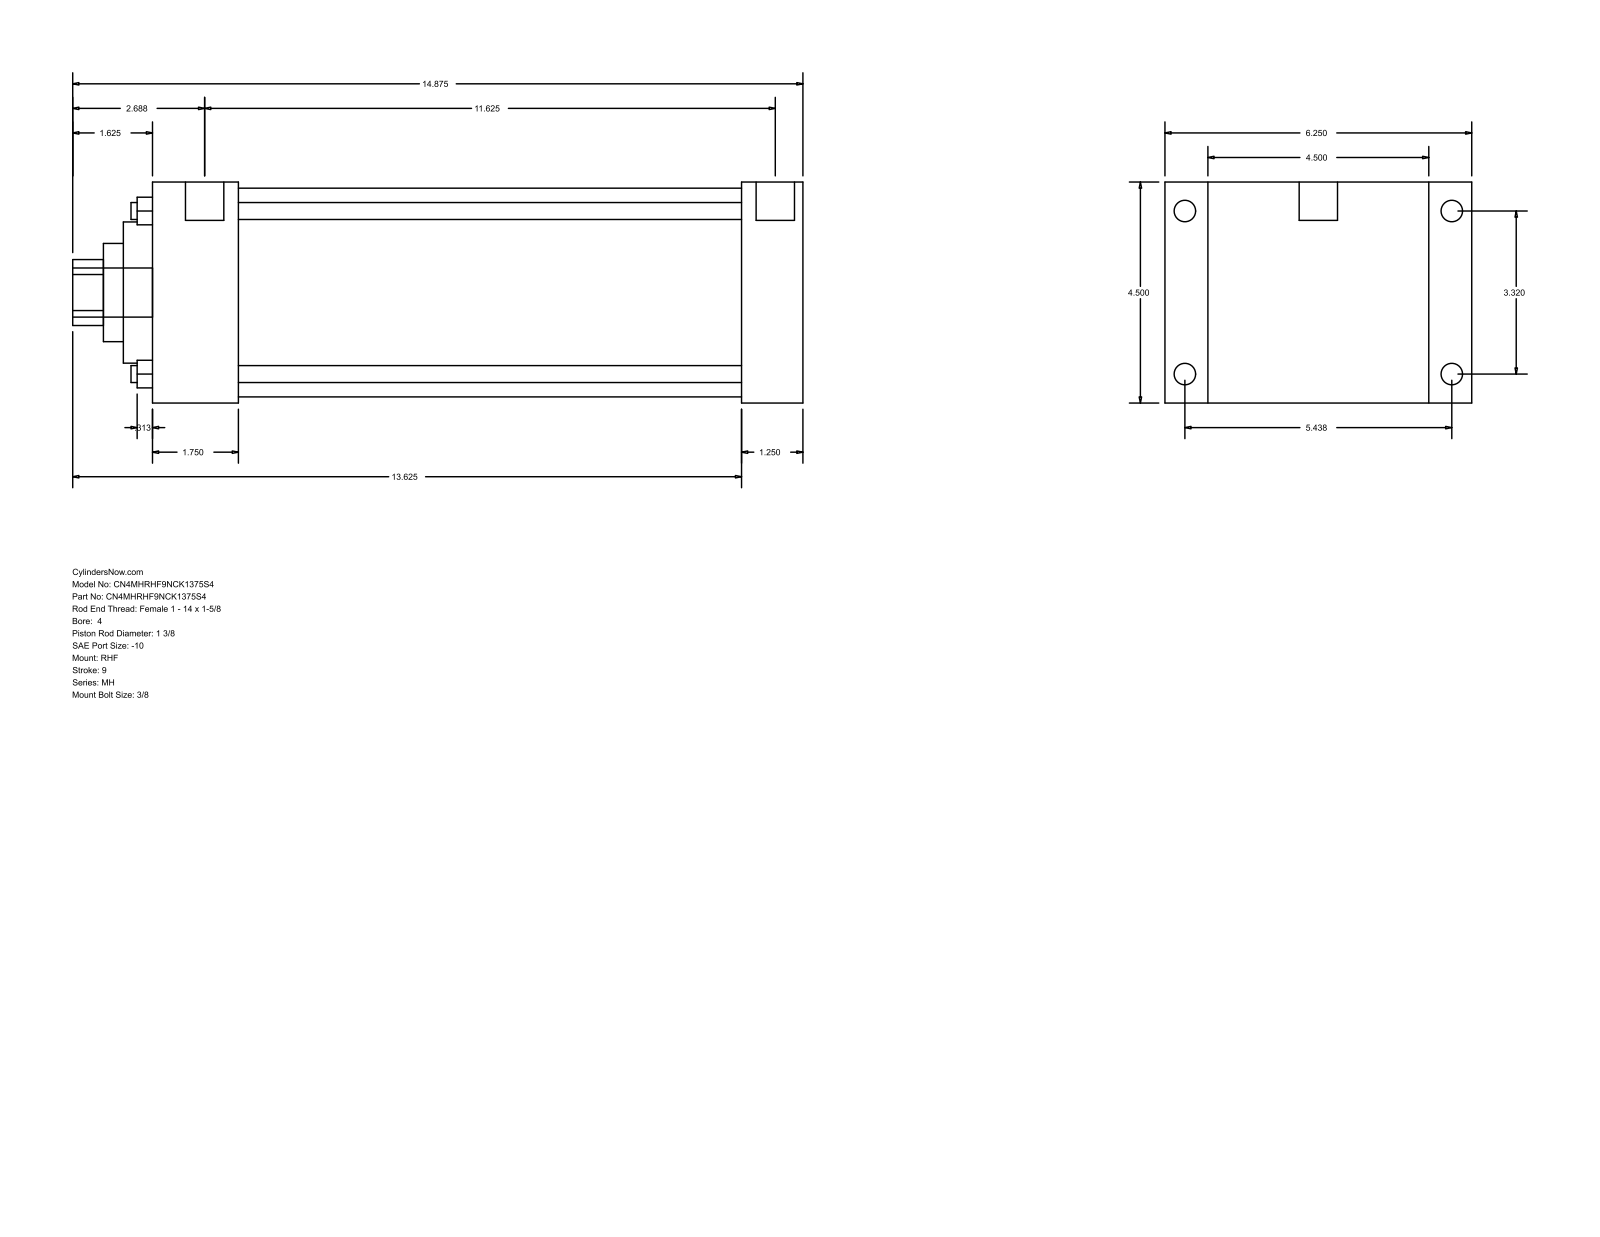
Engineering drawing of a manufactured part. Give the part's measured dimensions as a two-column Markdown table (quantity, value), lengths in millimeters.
| quantity | value |
| --- | --- |
| part name | MH_RHF__0400_1.375 |
| STEP written by | GSSL Pune (CONFIG_CONTROL_DESIGN) |
| units | millimeters |
| bodies | 0 solids, 90 faces (61 planar, 29 cylindrical, 0 other) |
| overall size | 377.82 × 158.75 × 114.3 |
| round holes (diameter × count) | 8.76 × 4, 34.92 × 1, 50.8 × 1, 73.03 × 1, 107.95 × 1 |
| round bosses / shafts (diameter × count) | 11.13 × 4, 8.73 × 4, 19.84 × 2, 25.4 × 1 |
| partial cylindrical surfaces (radius × count) | 17.06 × 1 |
| main face-to-face distances | 114.3, 336.55, 304.8, 31.75, 22.23, 136.53, 44.45, 260.35, 292.1, 158.76 |
| hole center spacings | 59.62, 84.32, 119.25 |
